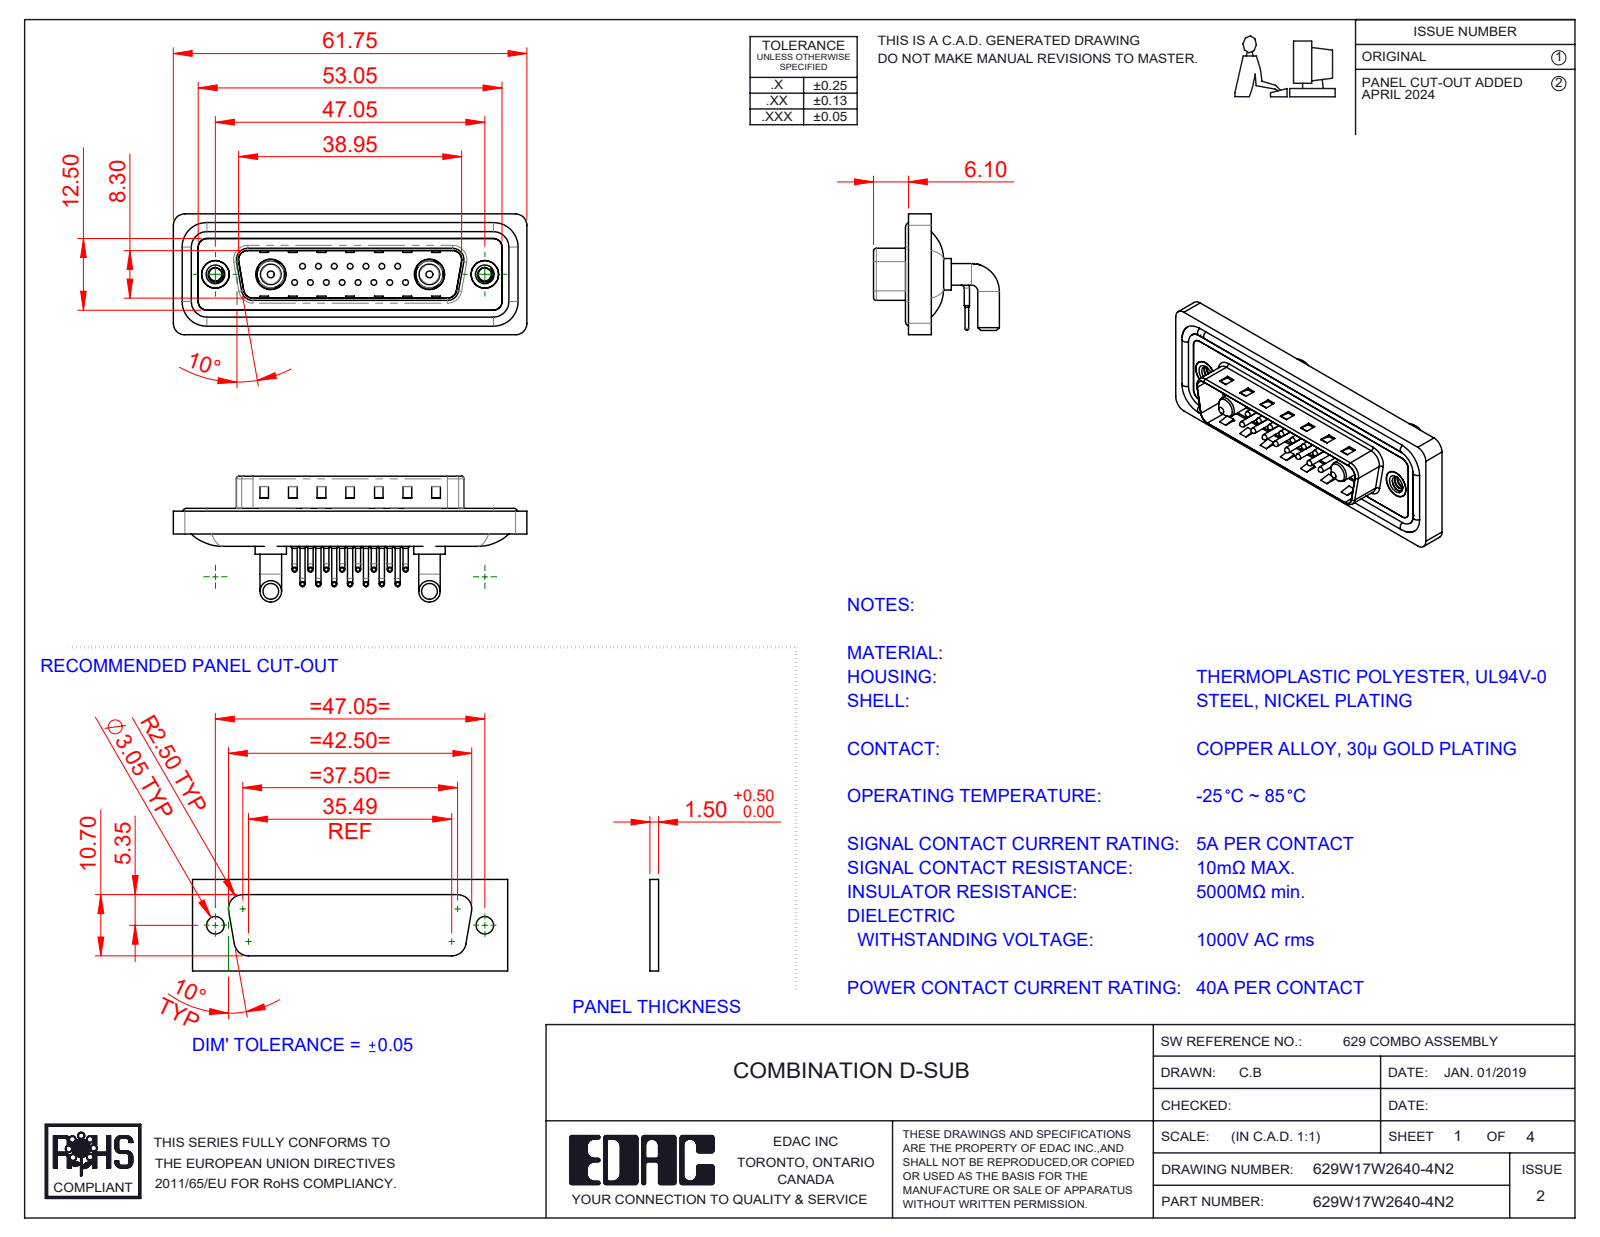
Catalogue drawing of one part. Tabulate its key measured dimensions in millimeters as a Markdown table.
| quantity | value |
| --- | --- |
| part name | 629Combo Shell Front_25 Contacts; 629Combo Shell Rear_25 Contacts; 629W17W2640-4N2; 629Combo Waterproof Housing_25 Contacts (+5 more) |
| STEP written by | SolidWorks 2023 (CONFIG_CONTROL_DESIGN) |
| units | millimeters |
| bodies | 26 solids, 2219 faces (1189 planar, 770 cylindrical, 260 other) |
| overall size | 61.75 × 21.98 × 21.1 |
| volume | 7 669 mm³ |
| surface area | 12 689 mm² |
| round holes (diameter × count) | 0.75 × 15, 1.6 × 15, 2 × 15, 2.26 × 2, 4 × 2, 4.8 × 2, 4.85 × 2, 5 × 2, 5.3 × 2 |
| round bosses / shafts (diameter × count) | 0.9 × 30, 1.5 × 15, 1 × 15, 0.65 × 15, 3.75 × 4, 1.6 × 4, 5.5 × 2, 5.2 × 2 |
| partial cylindrical surfaces (radius × count) | 1.5 × 18, 2 × 18, 1.01 × 15, 0.5 × 8, 1.6 × 8, 0.25 × 4, 0.6 × 4, 0.65 × 4 |
| main face-to-face distances | 0.4, 2.9, 0.8, 4.1, 1.1, 2.1, 1.6, 4.5, 1.5, 2.5 |
| hole center spacings | 3.16, 2.77, 5.54, 8.31, 5.04, 7.49, 11.08, 5.03 |
